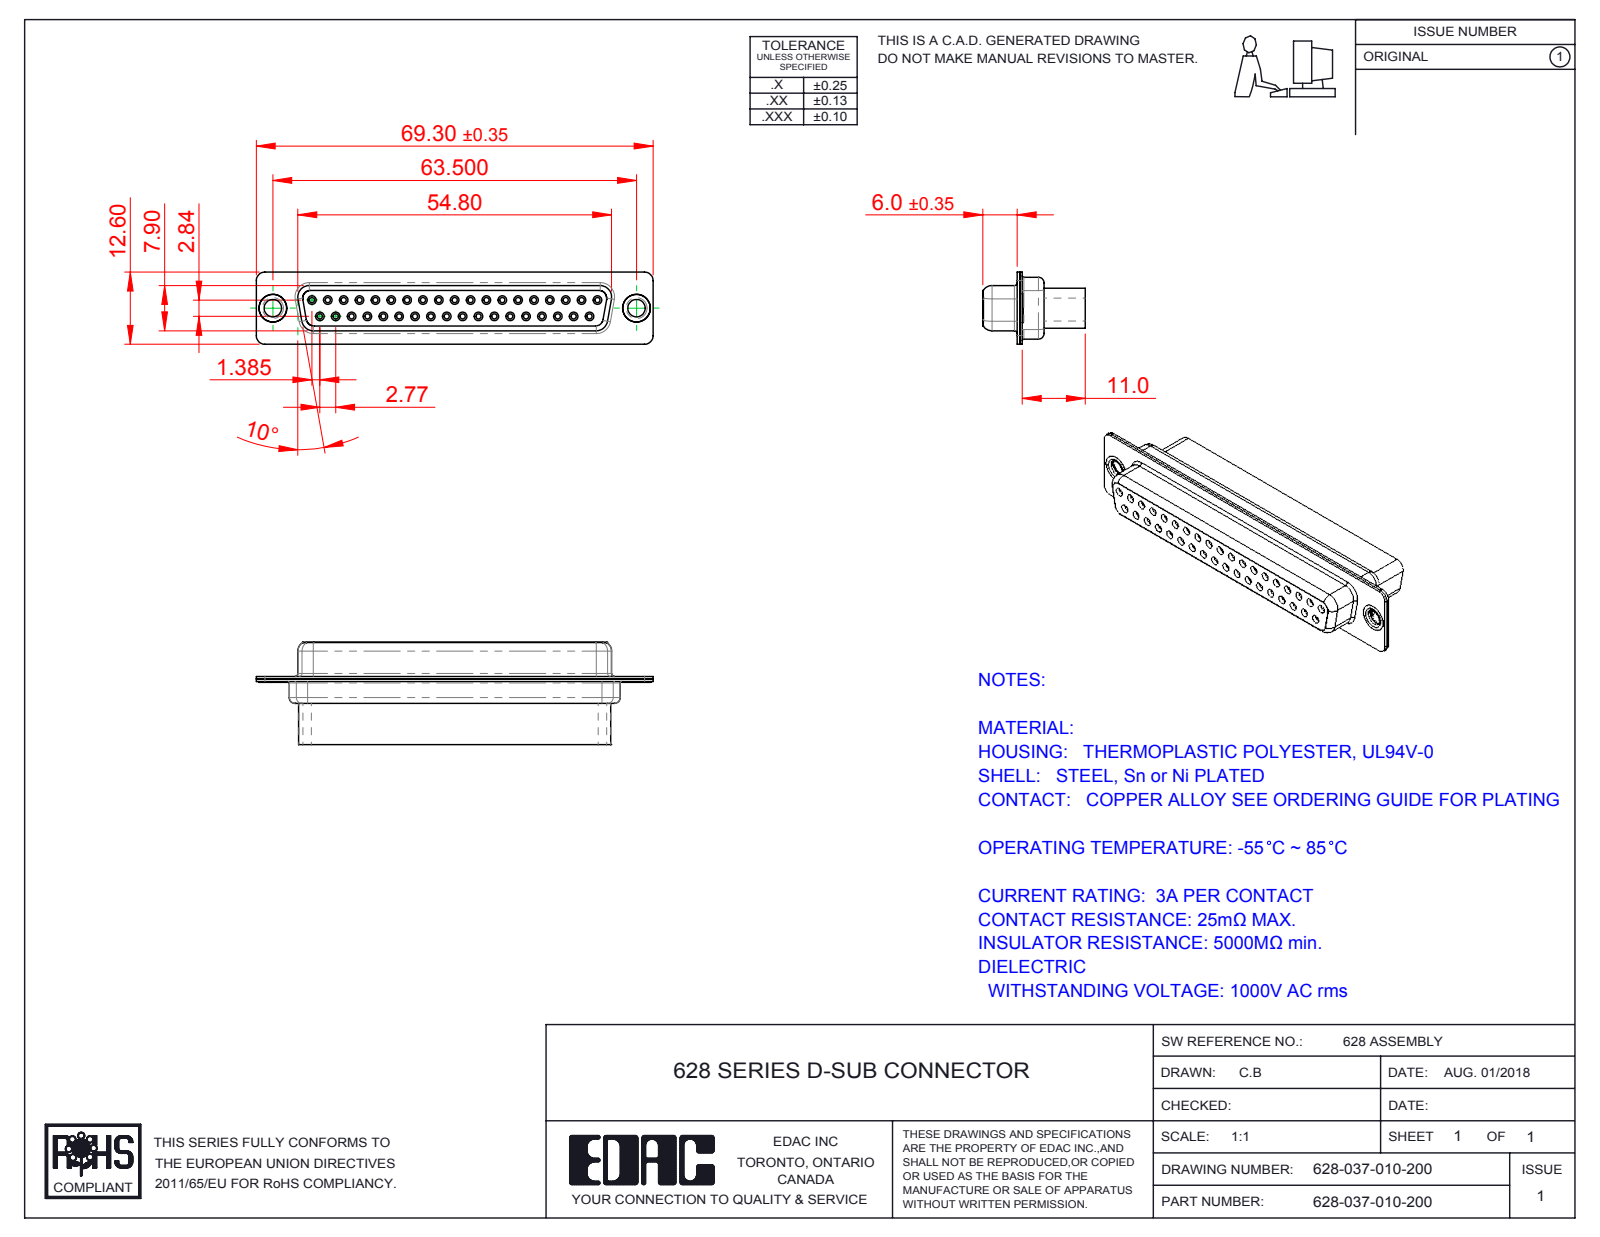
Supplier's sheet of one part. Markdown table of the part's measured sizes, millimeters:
| quantity | value |
| --- | --- |
| part name | 628 Shell Front_37 Contacts; 628 Thru Hole Rivet; 628 Shell Rear_37 Contacts; 628-050-010-200 (+1 more) |
| STEP written by | SolidWorks 2016 (CONFIG_CONTROL_DESIGN) |
| units | millimeters |
| bodies | 5 solids, 734 faces (178 planar, 417 cylindrical, 139 other) |
| overall size | 69.3 × 17.9 × 12.6 |
| volume | 6 587 mm³ |
| surface area | 10 809 mm² |
| round holes (diameter × count) | 0.9 × 37, 1.5 × 37, 2 × 37, 1.7 × 19, 1.6 × 18, 3.05 × 2, 4 × 2, 4.05 × 2, 4.85 × 2 |
| round bosses / shafts (diameter × count) | 5 × 2, 4.95 × 2, 4.8 × 2, 3.55 × 2 |
| partial cylindrical surfaces (radius × count) | 1.5 × 16, 2 × 12, 0.25 × 4, 0.5 × 4, 0.6 × 4, 0.65 × 4, 0.95 × 4, 1 × 4 |
| main face-to-face distances | 0.4, 0.45, 6.6, 7, 1.9, 8.5, 7.05, 0.85, 7.45, 1.4 |
| hole center spacings | 3.16, 2.77, 5.54, 8.31, 5.04, 7.49, 11.08, 13.85 |
